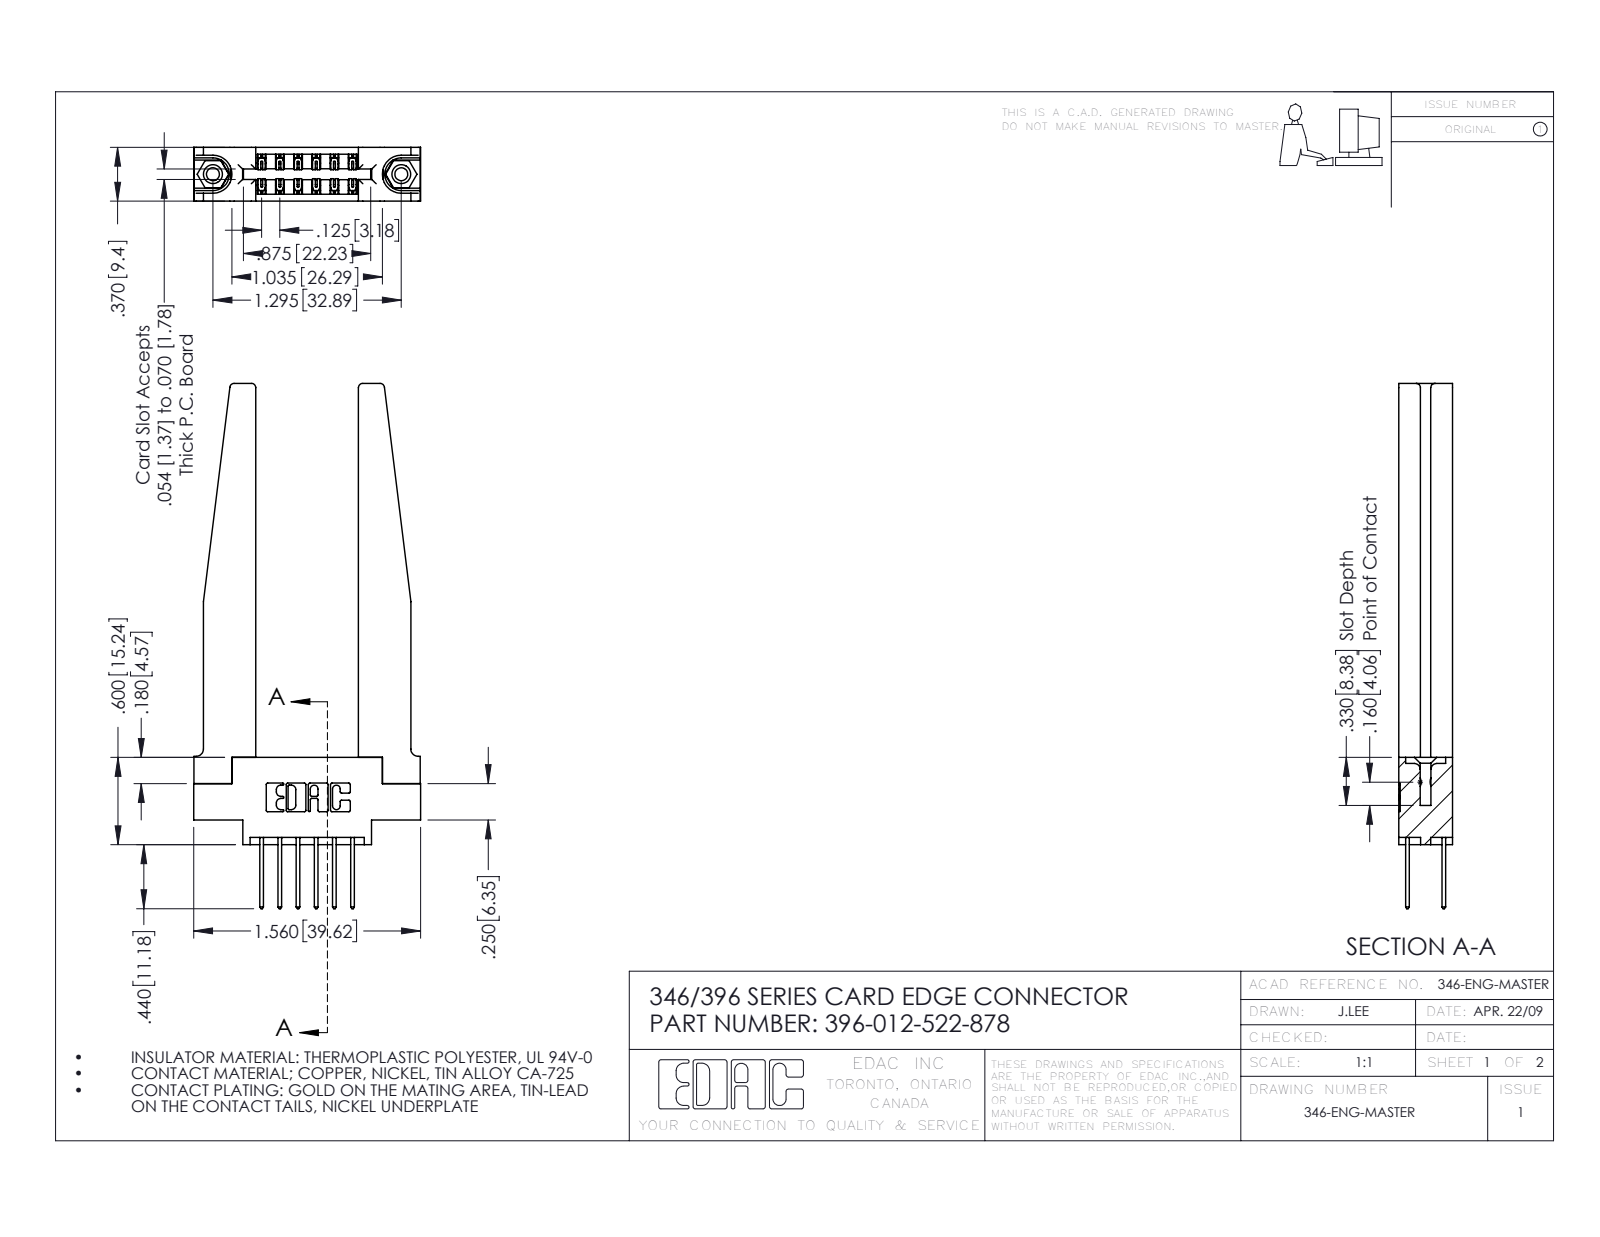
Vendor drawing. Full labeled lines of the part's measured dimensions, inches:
Part name (STEP PRODUCT): 345-292-001_345-293-122; 396-012-522-878; 346-220-078_345-220-078; 346 Part_0.170 Offset - 0.156 Dia-TH (+1 more)
STEP written by: SolidWorks 2016 (CONFIG_CONTROL_DESIGN)
Units: inches
Bodies: 17 solids, 984 faces (642 planar, 290 cylindrical, 52 other)
Overall size (bounding box): 3.61 × 1.56 × 0.37
Volume: 0.633 in³ · Surface area: 17.13 in²
Round holes (diameter × count): ⌀0.089 ×2, ⌀0.125 ×2, ⌀0.156 ×2, ⌀0.064 ×1
Round bosses / shafts (diameter × count): ⌀0.155 ×2
Partial cylindrical surfaces — rounded edges, fillets, slot ends (radius × count): R0.01 ×22, R0.006 ×18, R0.01 ×12, R0.03 ×8, R0.007 ×6, R0.031 ×6, R0.026 ×3, R0.014 ×2
Main face-to-face distances: 0.37, 0.15, 0.22, 0.25, 0.072, 0.148, 0.706, 0.102, 0.048, 0.322
Hole centre spacings: 0.246, 1.092, 1.295
